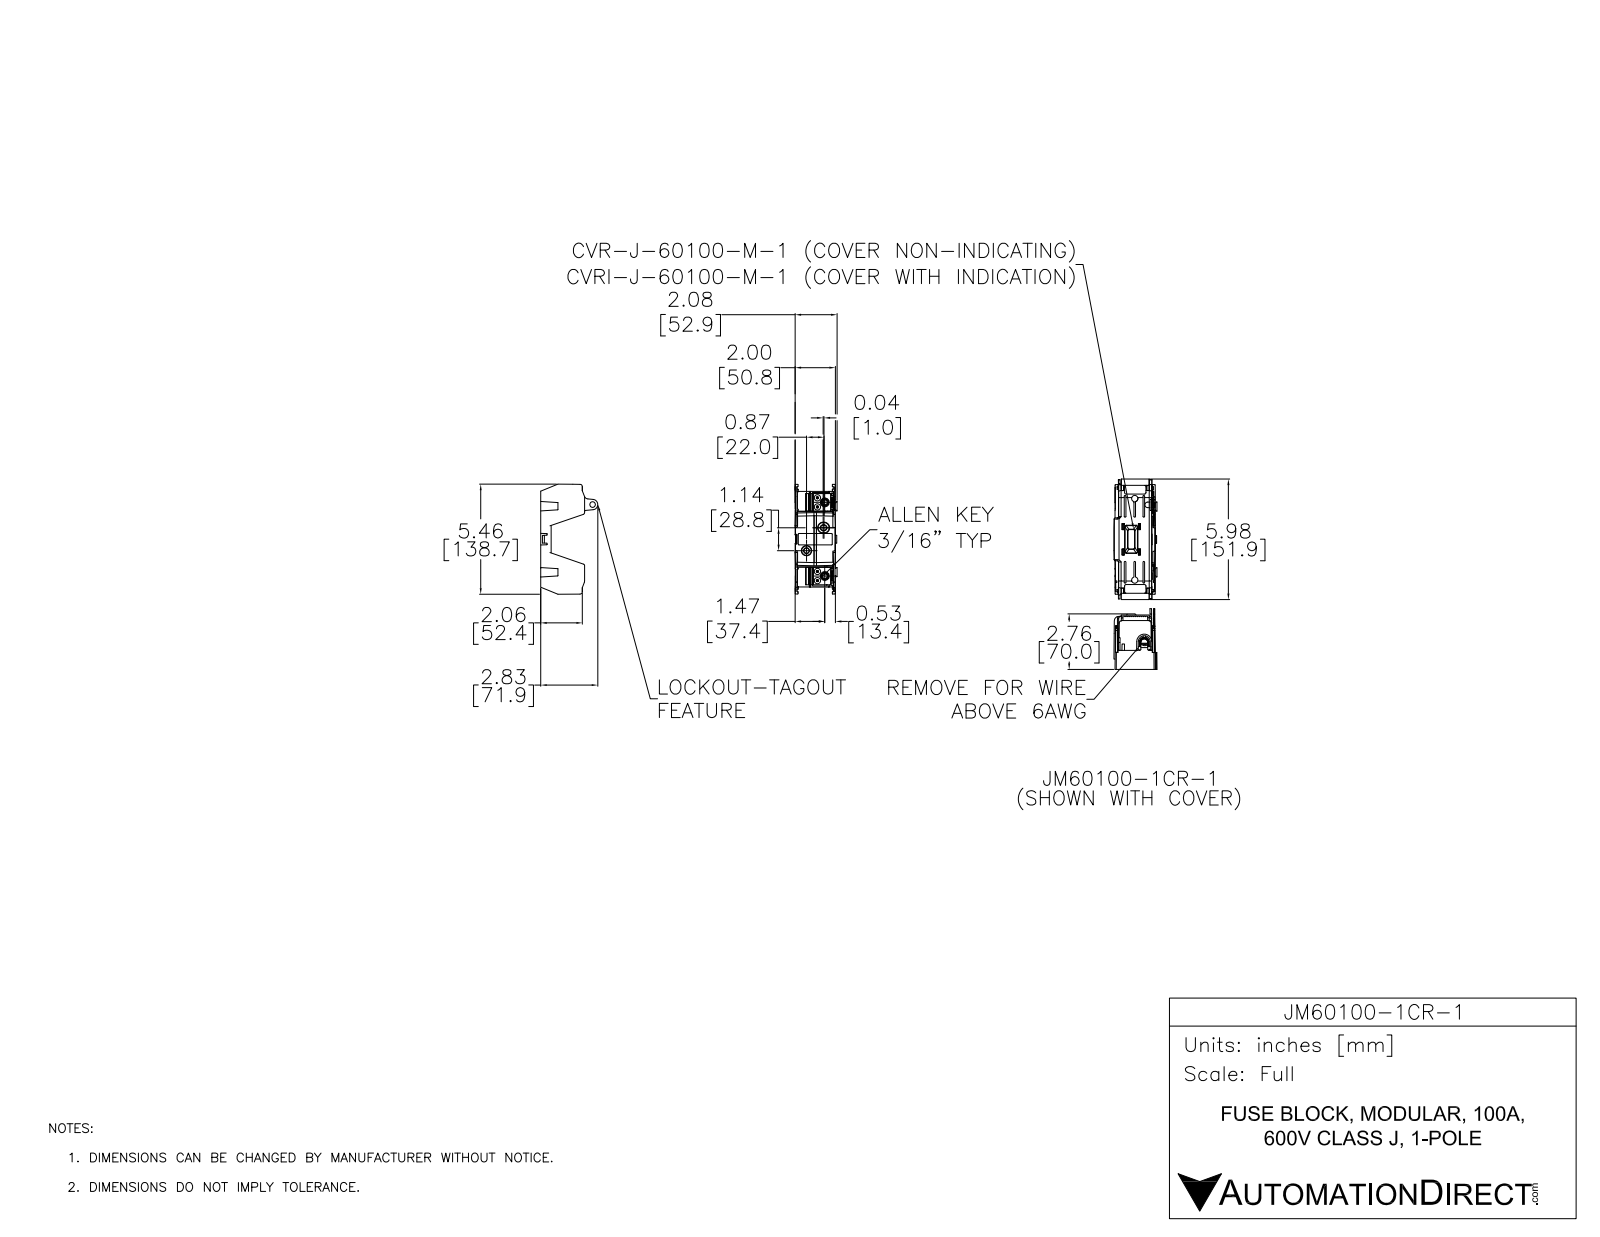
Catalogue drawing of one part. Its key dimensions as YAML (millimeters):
part_name: "JM60100-1CR-1"
step_written_by: "SolidWorks 2021 (CONFIG_CONTROL_DESIGN)"
units: millimeters
bodies: {solids: 0, faces: 881, planar: 281, cylindrical: 385, other: 215}
overall_size: [138.8, 71.9, 53.2]
round_holes:
  - {diameter: 4.8, count: 2}
  - {diameter: 6.4, count: 2}
round_bosses_or_shafts:
  - {diameter: 7.8, count: 4}
  - {diameter: 1, count: 4}
  - {diameter: 11.1, count: 2}
  - {diameter: 11.1, count: 2}
  - {diameter: 6, count: 2}
  - {diameter: 10.3, count: 1}
  - {diameter: 7, count: 1}
partial_cylinders:
  - {radius: 0.5, count: 77}
  - {radius: 0.3, count: 44}
  - {radius: 0.4, count: 36}
  - {radius: 0.5, count: 26}
  - {radius: 0.3, count: 23}
  - {radius: 0.8, count: 8}
  - {radius: 2, count: 8}
  - {radius: 4, count: 6}
face_to_face_distances: [48.2, 24.1, 0.6, 0.8, 93.3, 24.7, 0.6, 22.1, 46.7, 22.5]
hole_center_spacings: [93.3]
